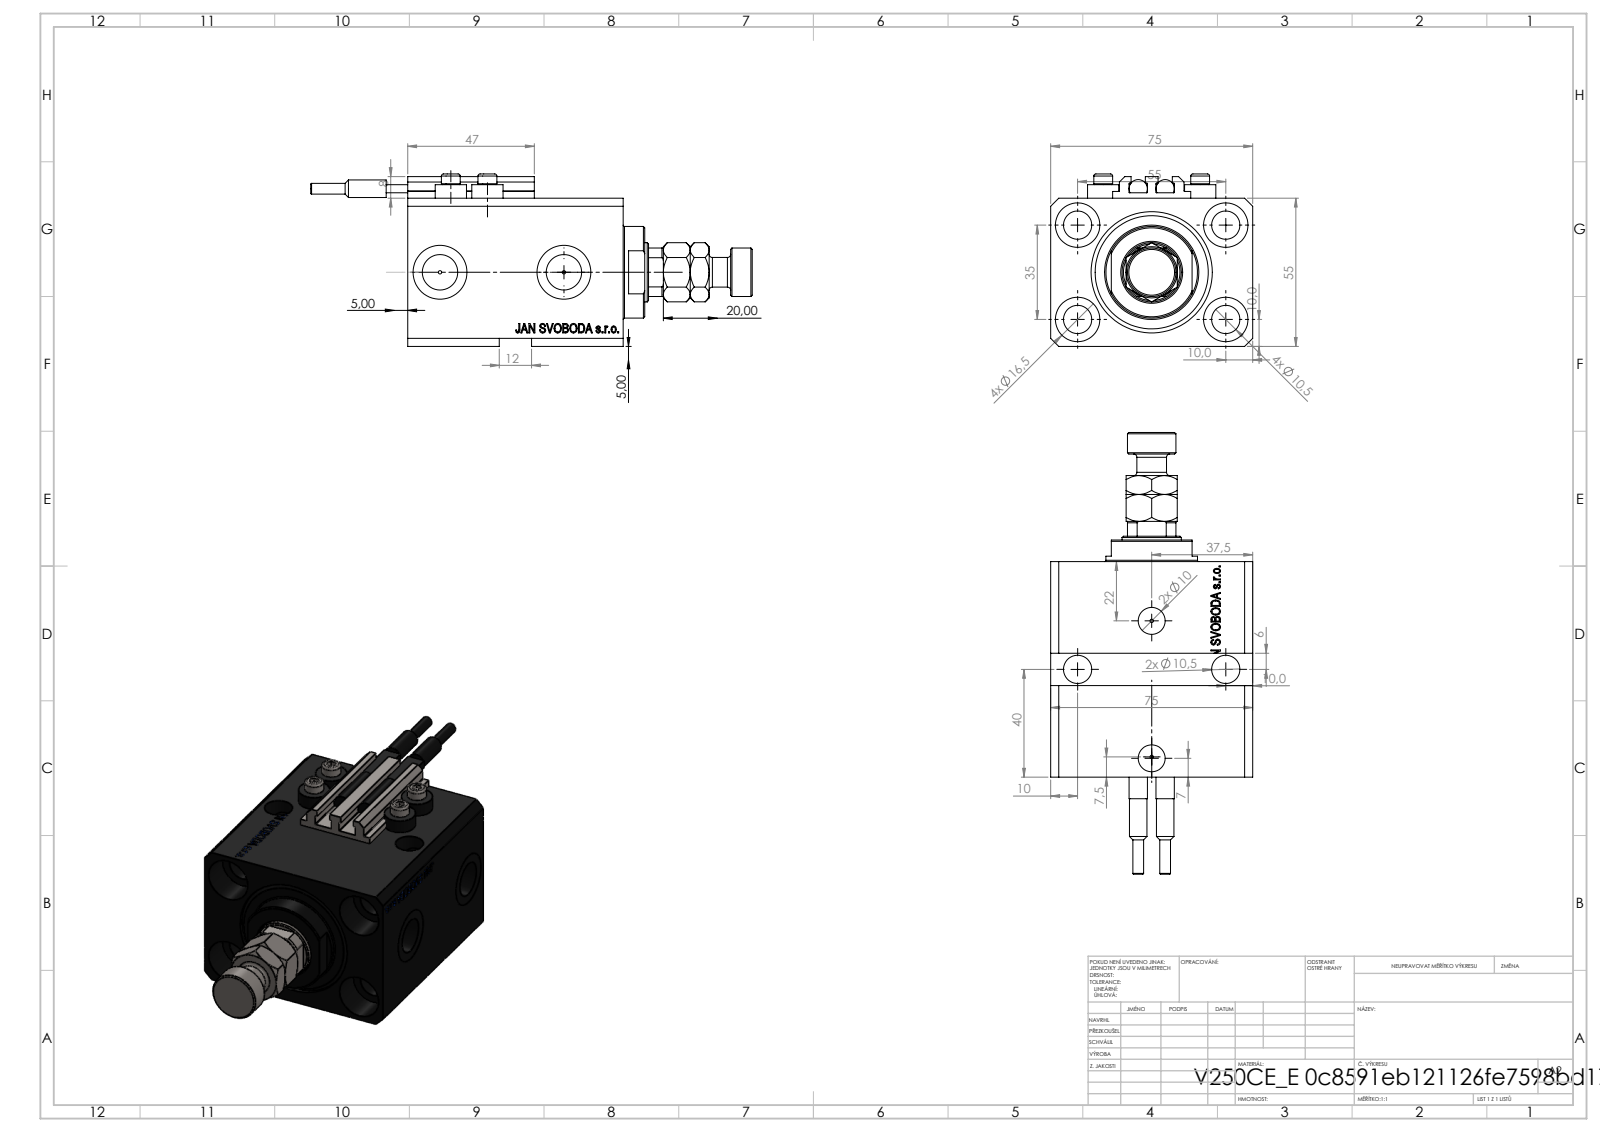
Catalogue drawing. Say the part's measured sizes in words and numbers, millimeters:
The part is named "V250CE_C_VCP; SWITCH_V250CE; V250CE_VC_E; V250CE_E_Body (+2 more)". Its 3-D file was written by "SolidWorks 2019 (CONFIG_CONTROL_DESIGN)". It is 11 solids with 1184 faces: 566 planar, 154 cylindrical and 464 other. Overall it measures 164 by 75 by 64 millimeters. Its volume is 291 915 cubic millimeters and its surface area 81 059 square millimeters. Round holes: 7 of diameter 10.5, 4 of diameter 1.25, 4 of diameter 4, 4 of diameter 16.5, 2 of diameter 10, 2 of diameter 13.16, 2 of diameter 20, 1 of diameter 22, 1 of diameter 32, 1 of diameter 45. Round bosses or shafts: 4 of diameter 11.6, 4 of diameter 7, 2 of diameter 6.8, 2 of diameter 6.5, 2 of diameter 4, 1 of diameter 34, 1 of diameter 18, 1 of diameter 11. Partial cylindrical surfaces (rounded edges, fillets, slot ends): 10 of radius 0.2, 1 of radius 10.5. The main face-to-face distances are 55, 75, 15, 80, 65, 3, 9.9, 55.1, 57, 70.1. The hole center spacings are 32.6, 55, 13.6, 14.09, 19.89, 20.12, 25.81, 28.48.
